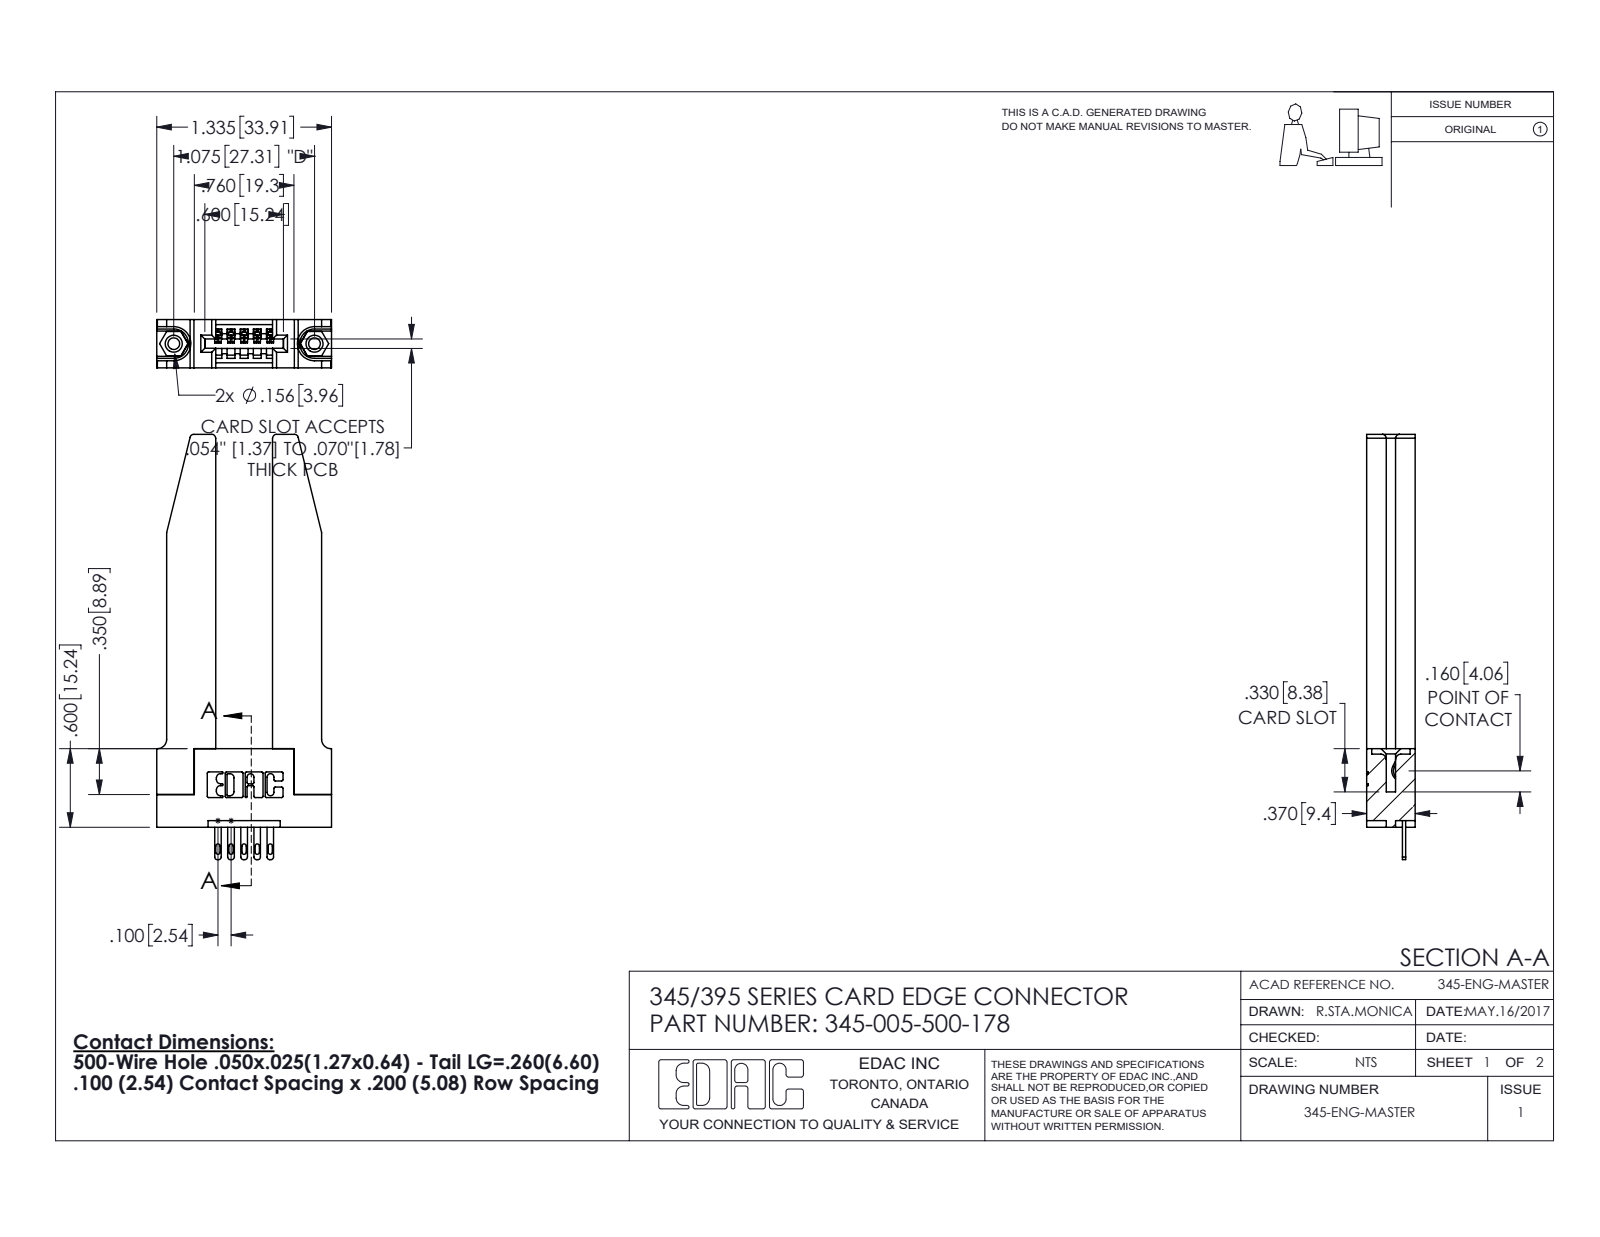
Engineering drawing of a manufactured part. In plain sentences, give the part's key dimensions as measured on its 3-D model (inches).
The part is named "345-292-001_345-293-100; 345 Part_Flush Mounting Lugs - 0.156 Dia-TH; 345-005-500-178; 345-220-078_345-220-078 (+1 more)". Its 3-D file was written by "SolidWorks 2016 (CONFIG_CONTROL_DESIGN)". It is 10 solids with 630 faces: 392 planar, 186 cylindrical and 52 other. Overall it measures 3.247 by 1.336 by 0.37 inches. Its volume is 0.653 cubic inches and its surface area 15.87 square inches. Round holes: 2 of diameter 0.089, 2 of diameter 0.125, 2 of diameter 0.156, 1 of diameter 0.064. Round bosses or shafts: 2 of diameter 0.155. Partial cylindrical surfaces (rounded edges, fillets, slot ends): 22 of radius 0.01, 10 of radius 0.006, 10 of radius 0.016, 10 of radius 0.02, 8 of radius 0.03, 6 of radius 0.007, 6 of radius 0.031, 3 of radius 0.026. The main face-to-face distances are 0.37, 0.15, 0.22, 0.435, 0.072, 0.148, 0.2, 0.077, 0.298, 0.095. The hole center spacings are 0.27, 0.847, 1.075.
